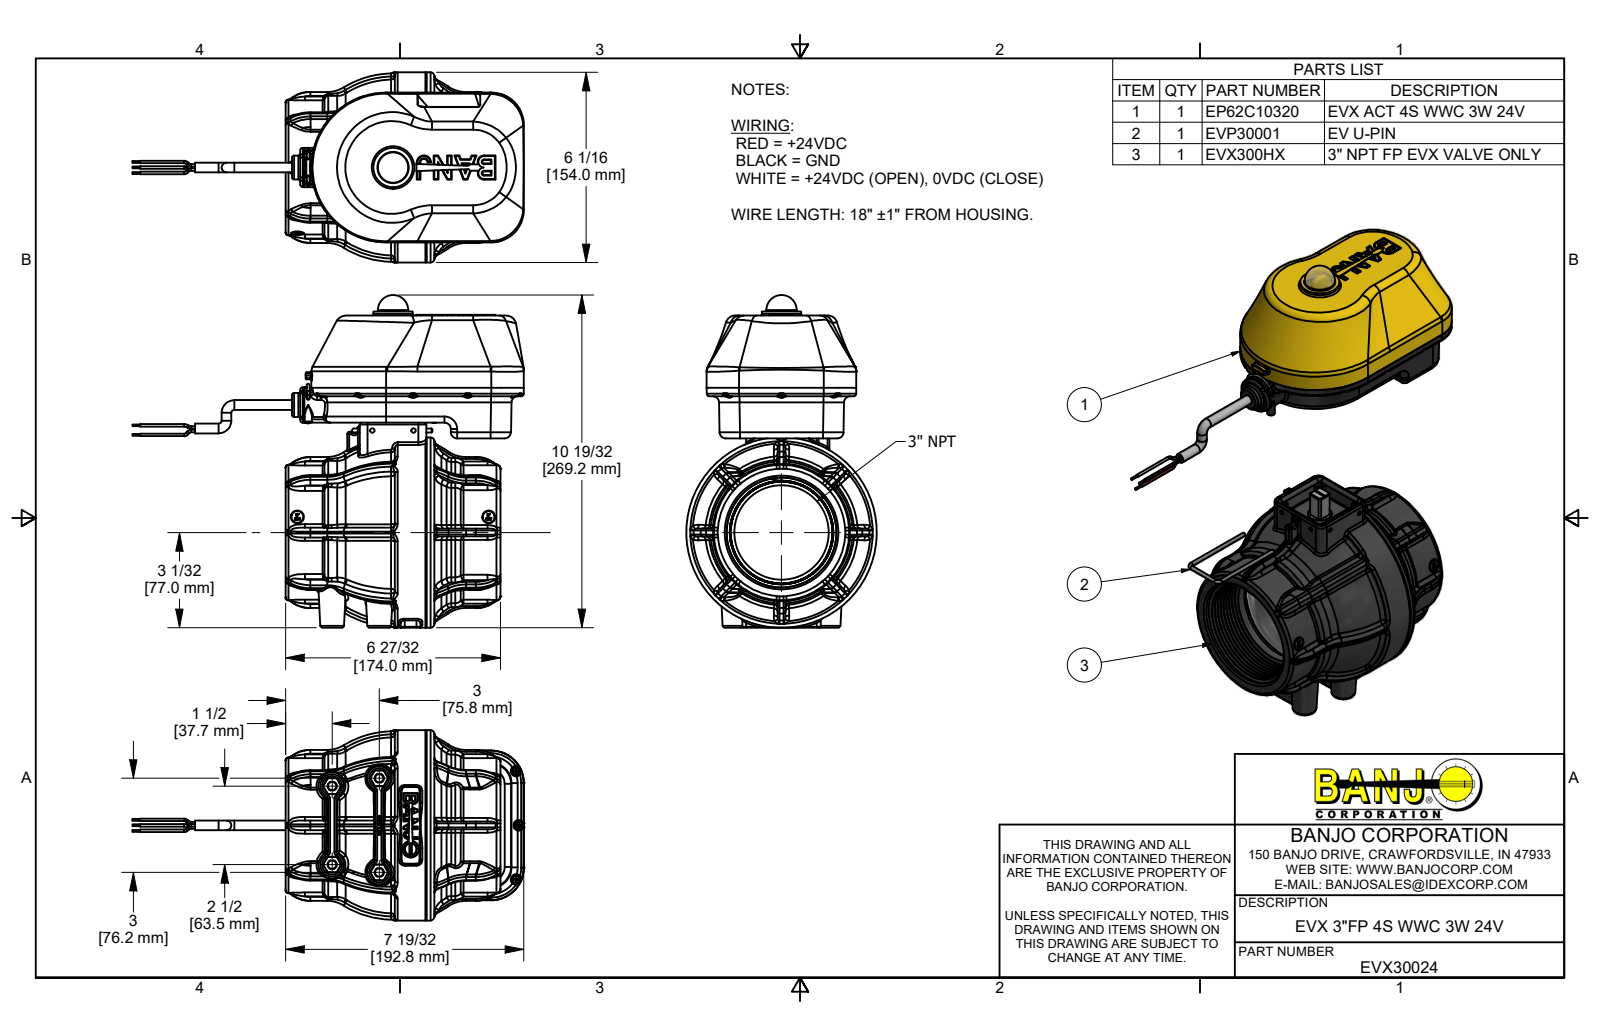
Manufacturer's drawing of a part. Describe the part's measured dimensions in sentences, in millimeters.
The part is named "EVX30024; EP62C10320; B61905PPHS; B632038PM (+8 more)". Its 3-D file was written by "Autodesk Inventor 2019 (AUTOMOTIVE_DESIGN)". It is 79 solids with 8941 faces: 2995 planar, 3246 cylindrical and 2700 other. Overall it measures 1555.9 by 269.2 by 154 millimeters. Its volume is 1 579 000 cubic millimeters and its surface area 1 774 000 square millimeters. Round holes: 15 of diameter 3.8, 11 of diameter 2.4, 11 of diameter 8.6, 7 of diameter 2, 6 of diameter 3.4, 4 of diameter 2.6, 4 of diameter 3.5, 4 of diameter 3.8, 4 of diameter 4.5, 4 of diameter 6.7, 4 of diameter 6.8, 4 of diameter 11. Round bosses or shafts: 19 of diameter 6.4, 15 of diameter 2, 11 of diameter 3.6, 11 of diameter 2.7, 11 of diameter 2.2, 6 of diameter 1.5, 4 of diameter 11.1, 4 of diameter 9.5. Partial cylindrical surfaces (rounded edges, fillets, slot ends): 204 of radius 0.3, 138 of radius 10.3, 114 of radius 9.8, 112 of radius 7.8, 108 of radius 6.4, 106 of radius 15.5, 96 of radius 0.3, 76 of radius 3.2. The main face-to-face distances are 2.1, 12.7, 2.2, 3.2, 4.6, 2.4, 55.2, 57.7, 59.8, 58.4. The hole center spacings are 84.2, 57.7, 58.6, 61.6, 26.5, 33.4, 107.8, 108.9.
